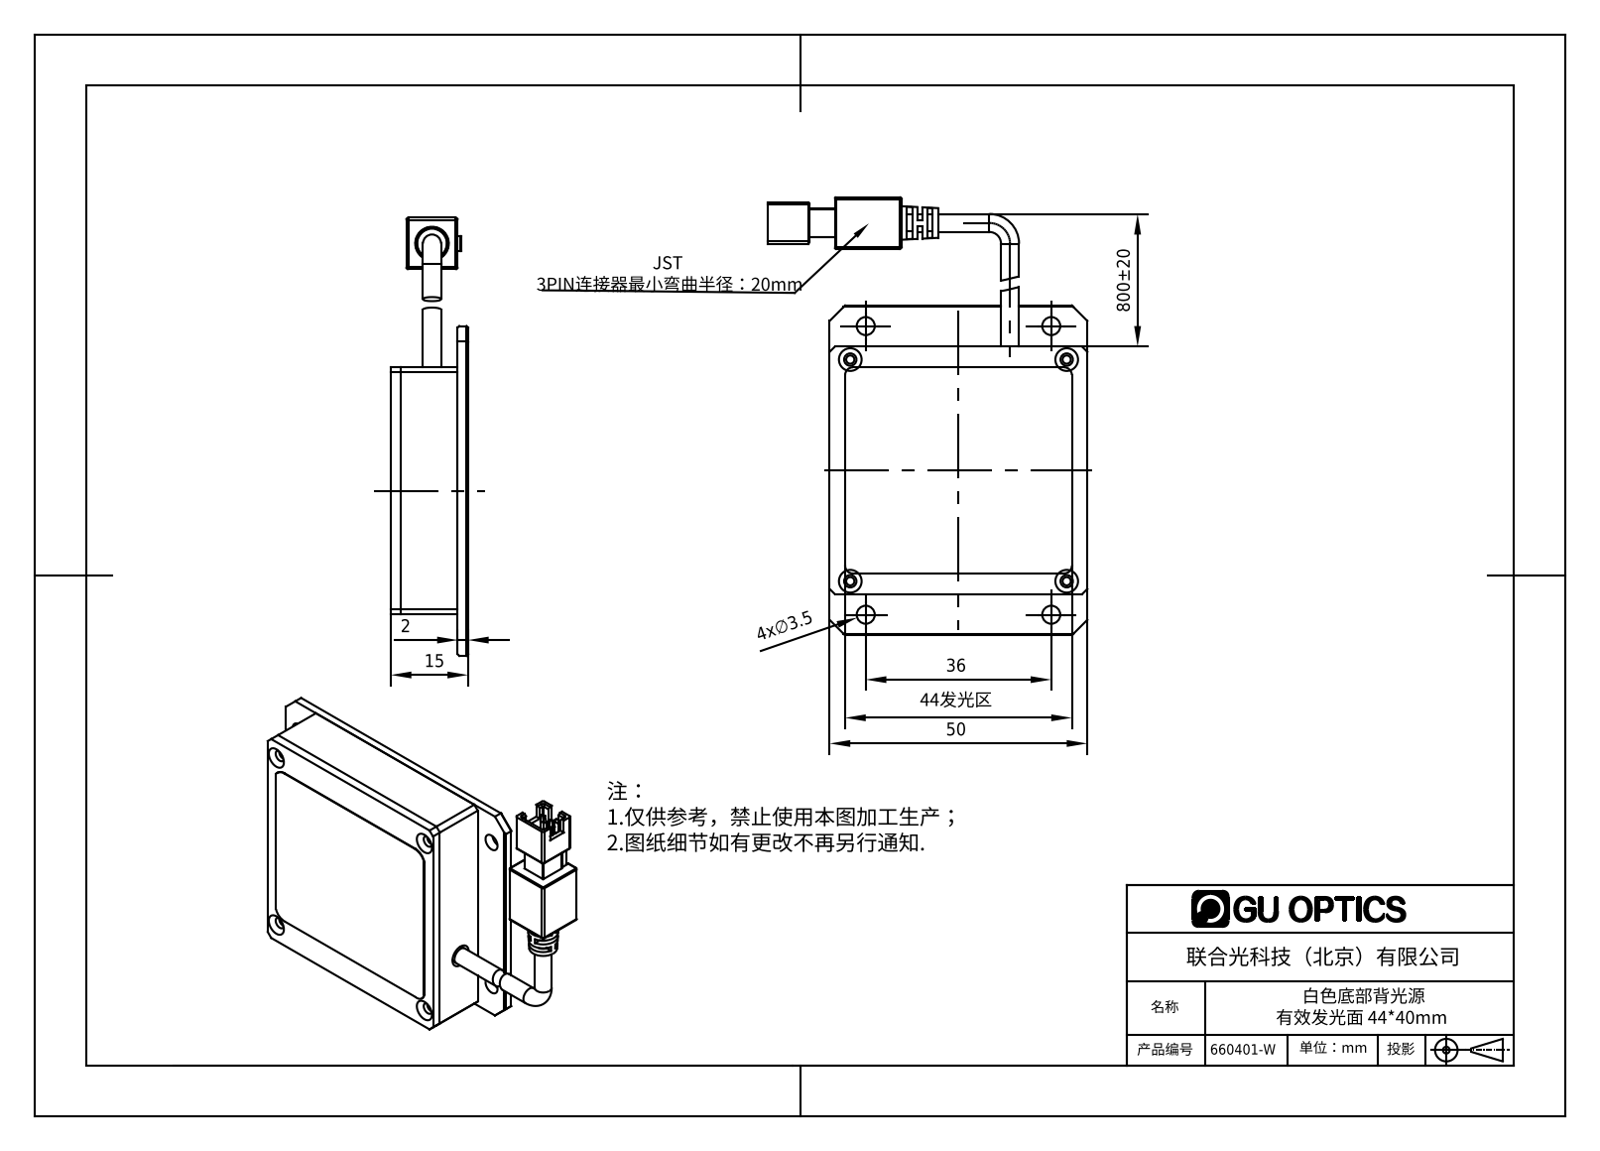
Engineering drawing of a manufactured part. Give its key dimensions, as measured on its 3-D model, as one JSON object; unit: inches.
{"part_name": "660401-W", "step_written_by": "SolidWorks 2016 (AUTOMOTIVE_DESIGN)", "units": "inches", "bodies": {"solids": 6, "faces": 476, "planar": 239, "cylindrical": 118, "other": 119}, "overall_size": [3.346, 2.441, 0.594], "volume_in3": 1.326, "surface_area_in2": 36.46, "round_holes": [[0.063, 8], [0.094, 8], [0.138, 4]], "round_bosses_or_shafts": [[0.138, 2]], "partial_cylinders_radius": [[0.004, 15], [0.008, 13], [0.016, 12], [0.059, 6], [0.039, 4], [0.012, 1], [0.027, 1], [0.055, 1]], "face_to_face_distances": [0.079, 0.512, 0.433, 0.118, 0.039, 0.394, 0.083, 0.476, 0.594, 0.516], "hole_center_spacings": [0.039, 0.246, 0.282, 1.551, 1.557, 1.654, 1.654, 1.732]}
